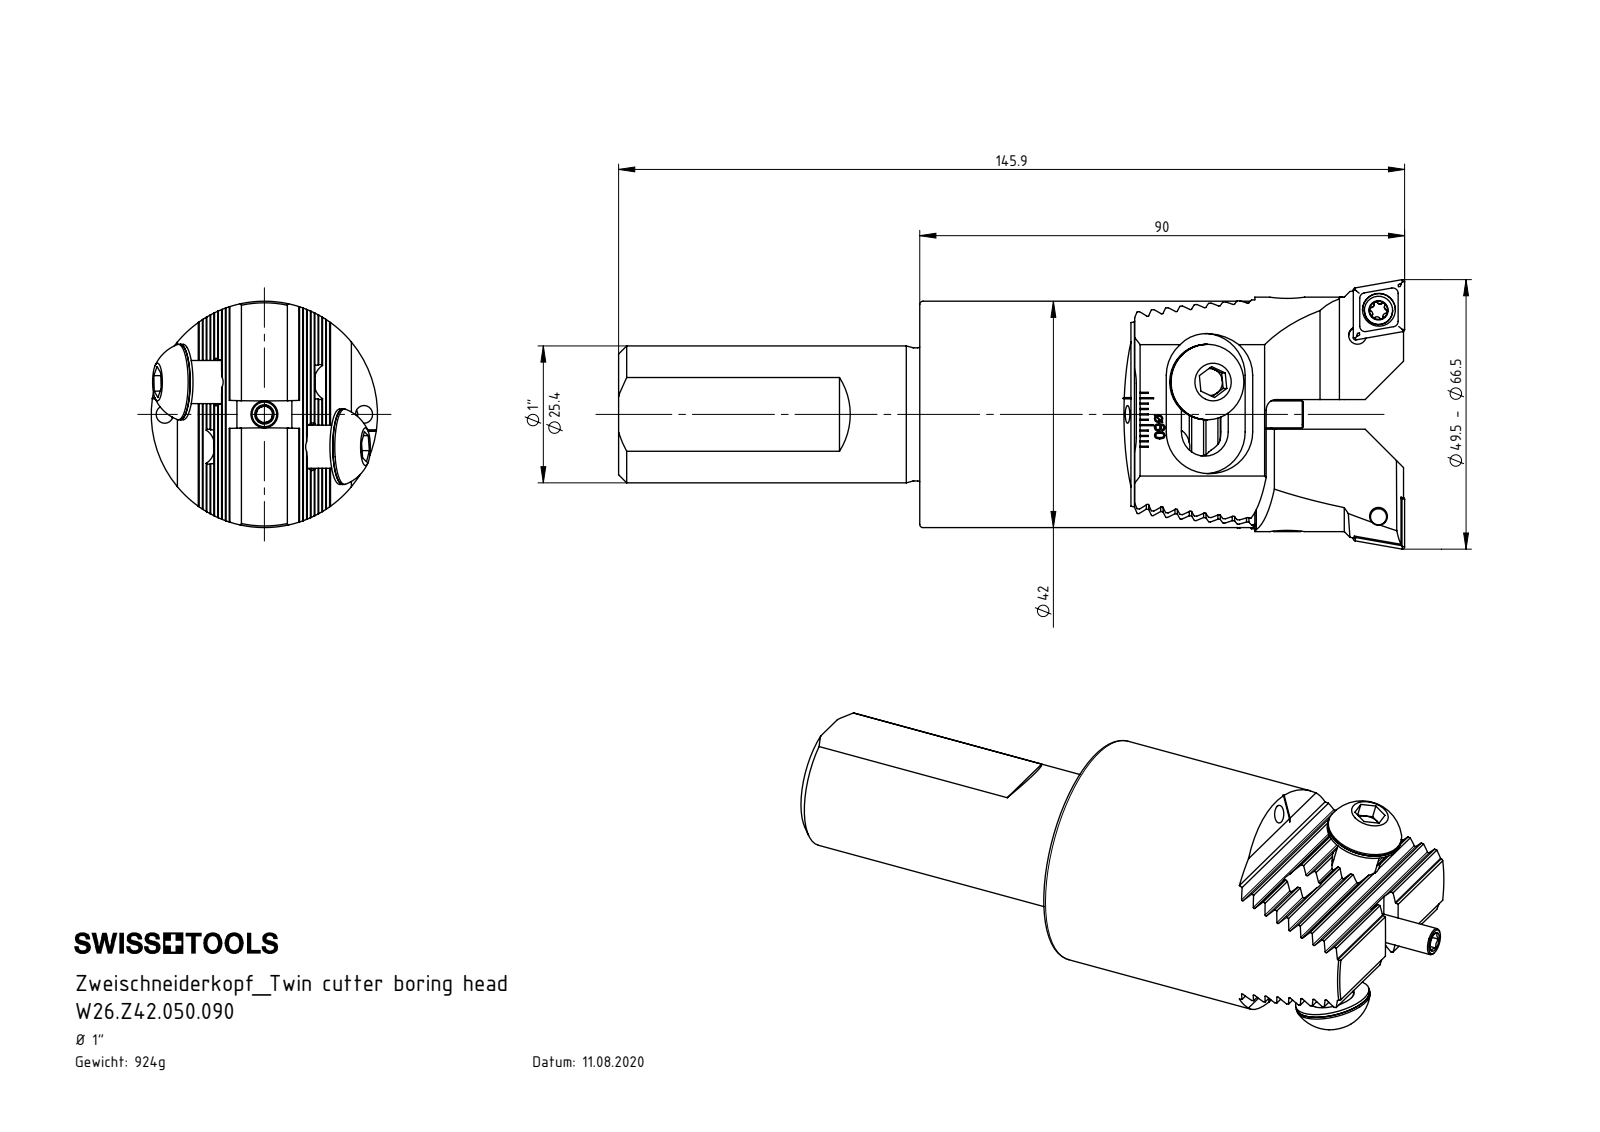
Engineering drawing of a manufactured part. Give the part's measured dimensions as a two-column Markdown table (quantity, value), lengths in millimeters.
| quantity | value |
| --- | --- |
| part name | Z42-ER1.002.020_A; Z42-WCB.001.028; Z42-WCB.001.028_A; CCMT09T304 (+6 more) |
| STEP written by | SolidWorks 2022 (CONFIG_CONTROL_DESIGN) |
| units | millimeters |
| bodies | 13 solids, 737 faces (326 planar, 236 cylindrical, 175 other) |
| overall size | 145.9 × 49.5 × 42 |
| volume | 117 148 mm³ |
| surface area | 35 347 mm² |
| round holes (diameter × count) | 3.3 × 8, 1 × 2, 4.4 × 2, 6.1 × 2, 6.8 × 2, 8.4 × 2, 9 × 2, 5 × 1, 10.7 × 1, 13.5 × 1 |
| round bosses / shafts (diameter × count) | 4 × 3, 14 × 2, 8 × 2, 5.25 × 2, 42 × 1, 25.4 × 1, 24.7 × 1, 6 × 1 |
| partial cylindrical surfaces (radius × count) | 0.2 × 34, 0.34 × 12, 0.59 × 12, 1 × 8, 0.5 × 4, 4.5 × 4, 8 × 4, 9 × 2 |
| main face-to-face distances | 2.38, 14.29, 4.76, 11.91, 7.14, 4.77, 9.53, 9.52, 2.31, 16.67 |
| hole center spacings | 6.11, 6.26, 13, 33.59, 33.71, 38.15, 25.12, 28.68 |
